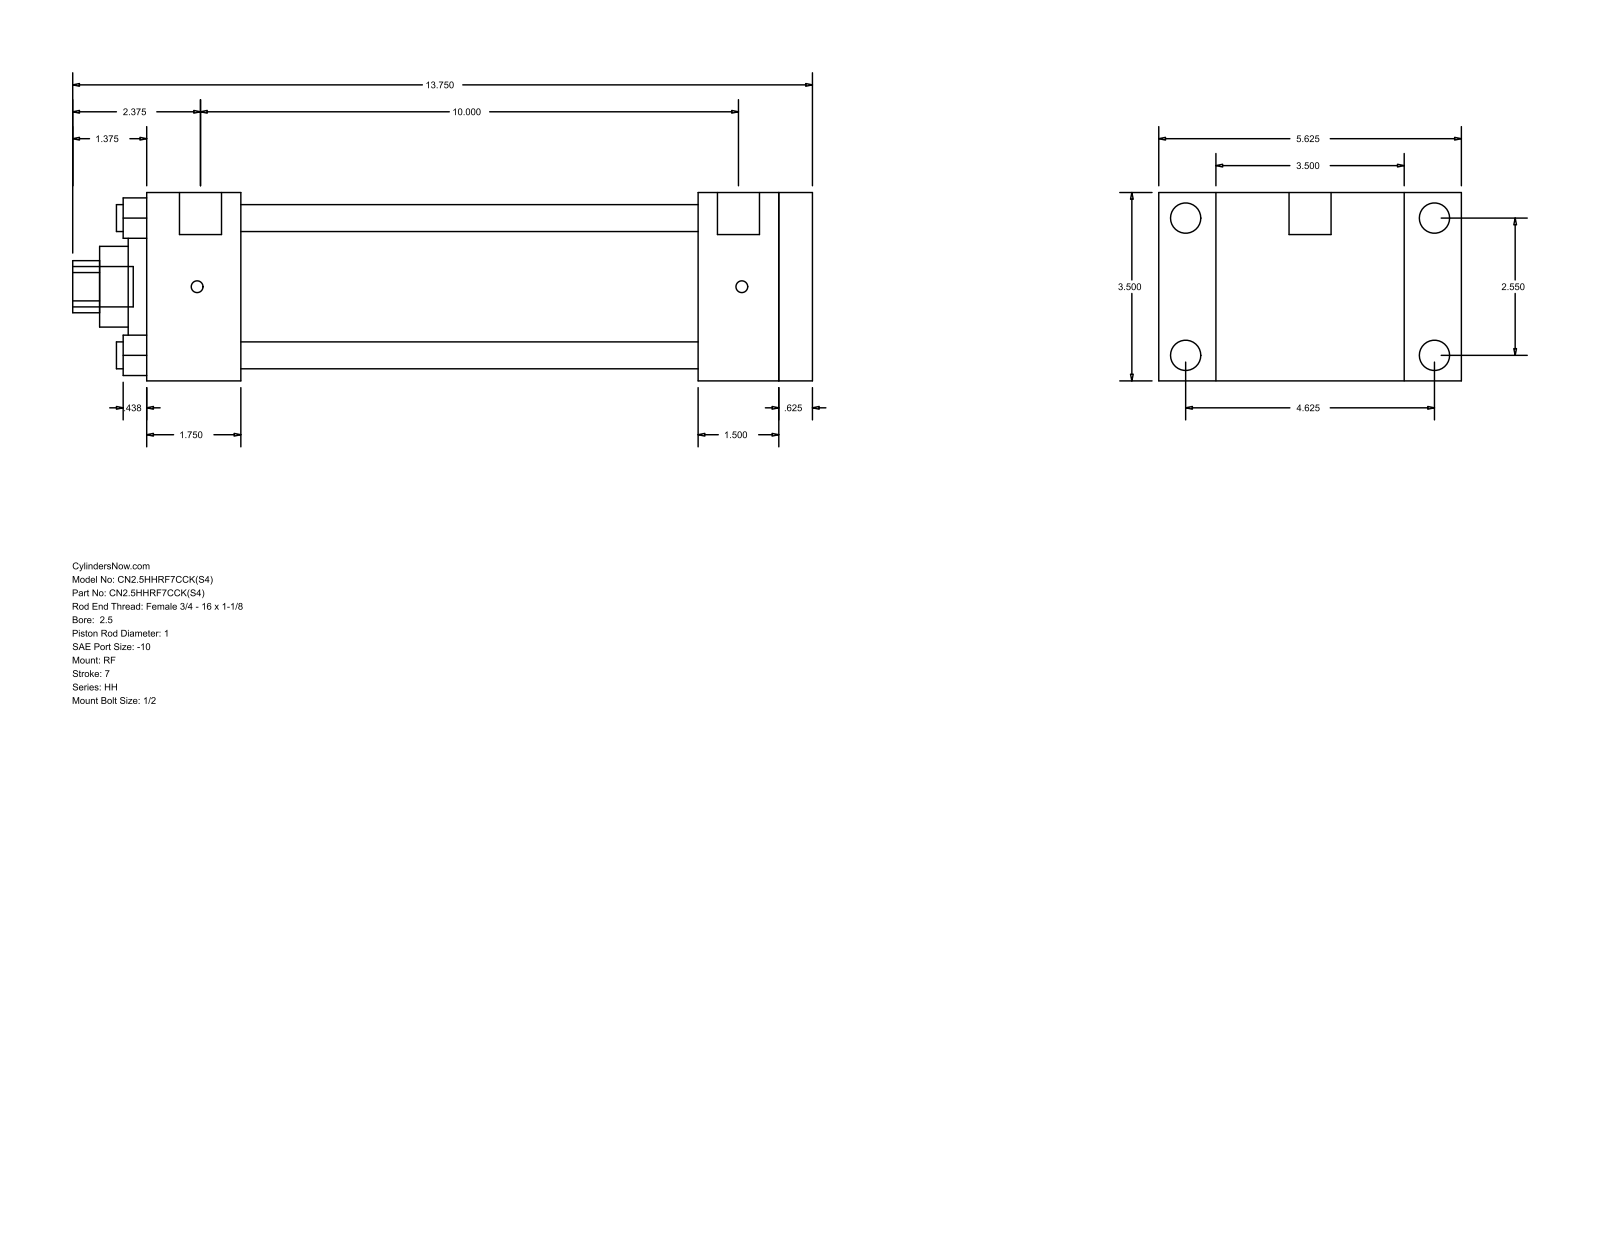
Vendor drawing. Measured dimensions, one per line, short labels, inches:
name: HH_RF__0250_1
written by: GSSL Pune (CONFIG_CONTROL_DESIGN)
unit: in
bodies: 0 solids, 94 faces (65 planar, 29 cylindrical, 0 other)
size: 13.75 × 5.625 × 3.5
holes: 4× ⌀0.5, 1× ⌀1, 1× ⌀1.5, 1× ⌀2.375, 1× ⌀2.875
bosses: 4× ⌀0.563, 4× ⌀0.219, 2× ⌀0.781, 1× ⌀0.75
rounds: 1× R0.484
face distances: 3.5, 0.625, 11.75, 12.375, 1.75, 10, 10.625, 10.25, 8.5, 1.5
hole spacings: 1.803, 2.55, 3.606
